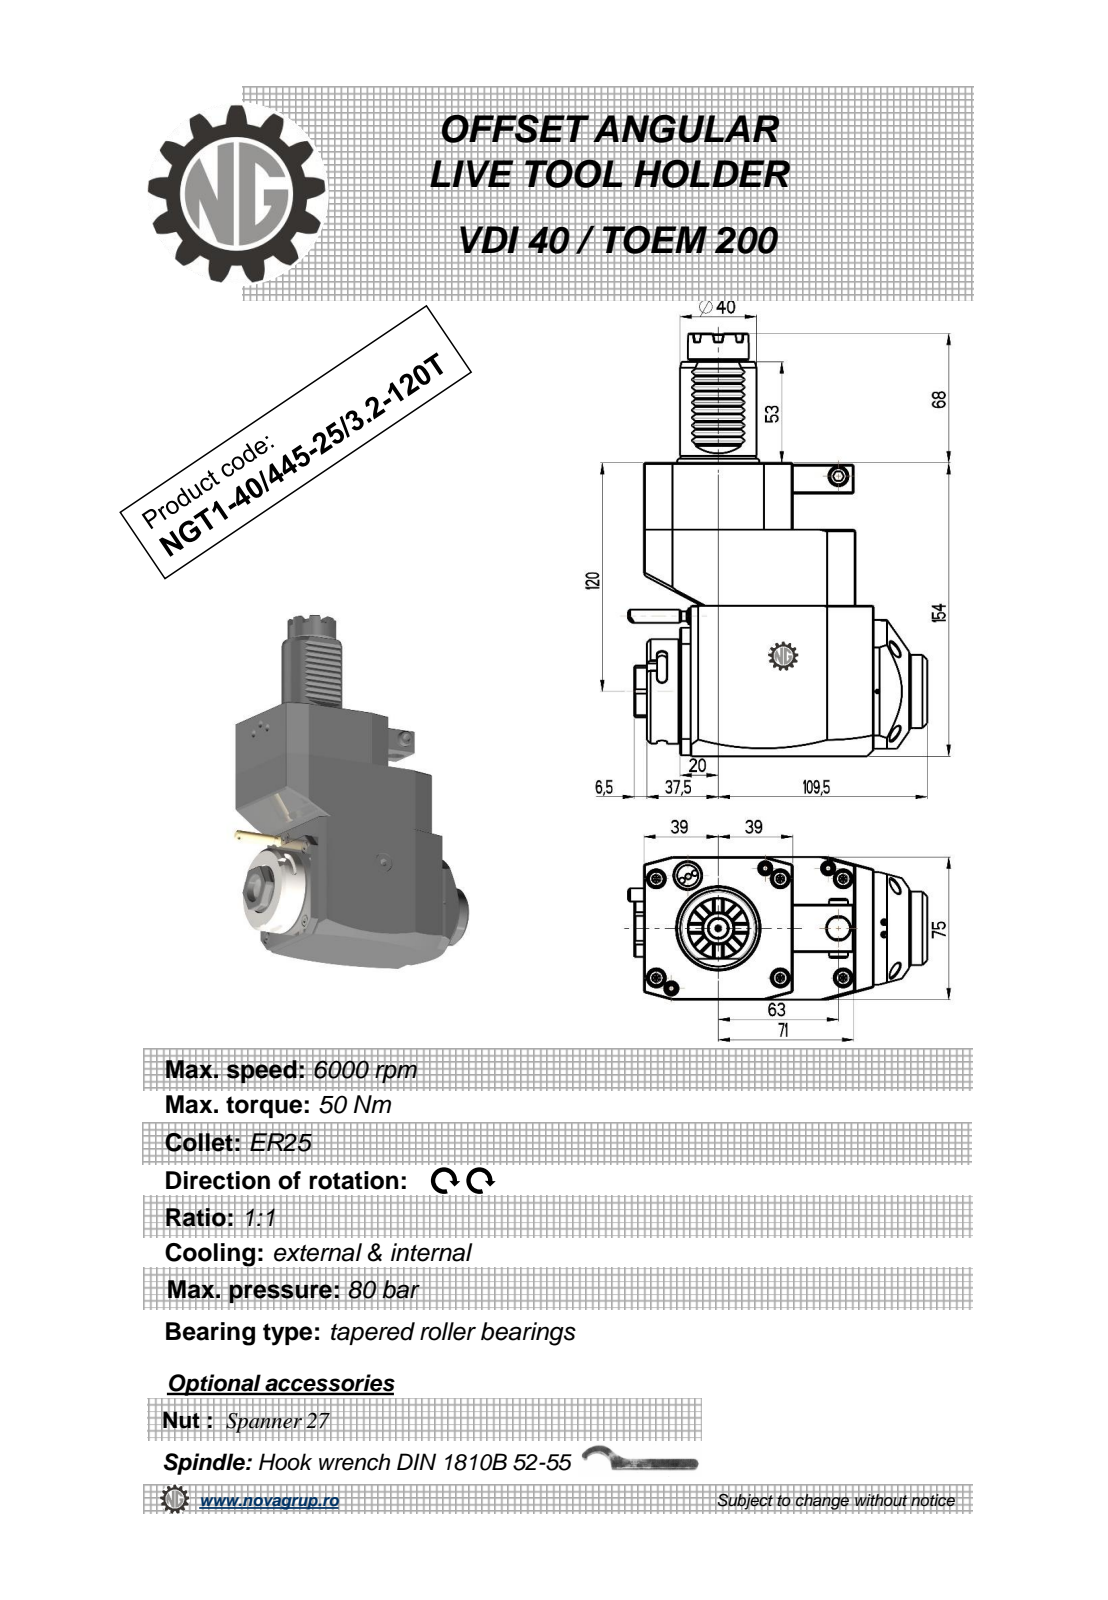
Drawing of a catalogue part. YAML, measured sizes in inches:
part_name: "NGT1_40_445_25_3_2_120T"
step_written_by: "PRO/ENGINEER BY PARAMETRIC TECHNOLOGY CORPORATION, 2010280 (CONFIG_CONTROL_DESIGN)"
units: inches
bodies: {solids: 1, faces: 415, planar: 225, cylindrical: 80, other: 110}
overall_size: [8.74, 6.174, 2.953]
volume: 77.93
surface_area: 140.2
round_holes:
  - {diameter: 0.098, count: 1}
  - {diameter: 0.118, count: 1}
  - {diameter: 0.335, count: 1}
  - {diameter: 0.374, count: 1}
  - {diameter: 0.472, count: 1}
  - {diameter: 0.709, count: 1}
round_bosses_or_shafts:
  - {diameter: 0.353, count: 2}
  - {diameter: 2.165, count: 1}
  - {diameter: 1.89, count: 1}
  - {diameter: 1.575, count: 1}
  - {diameter: 1.516, count: 1}
  - {diameter: 1.26, count: 1}
  - {diameter: 0.661, count: 1}
  - {diameter: 0.394, count: 1}
partial_cylinders:
  - {radius: 0.012, count: 10}
  - {radius: 0.098, count: 6}
  - {radius: 7.087, count: 2}
  - {radius: 0.02, count: 1}
  - {radius: 0.339, count: 1}
  - {radius: 0.591, count: 1}
  - {radius: 0.965, count: 1}
  - {radius: 1.476, count: 1}
face_to_face_distances: [2.953, 6.063, 4.685, 0.748, 2.323, 4.37, 1.378, 3.622, 0.689, 3.071]
hole_center_spacings: [1.701, 2.956, 4.429]
